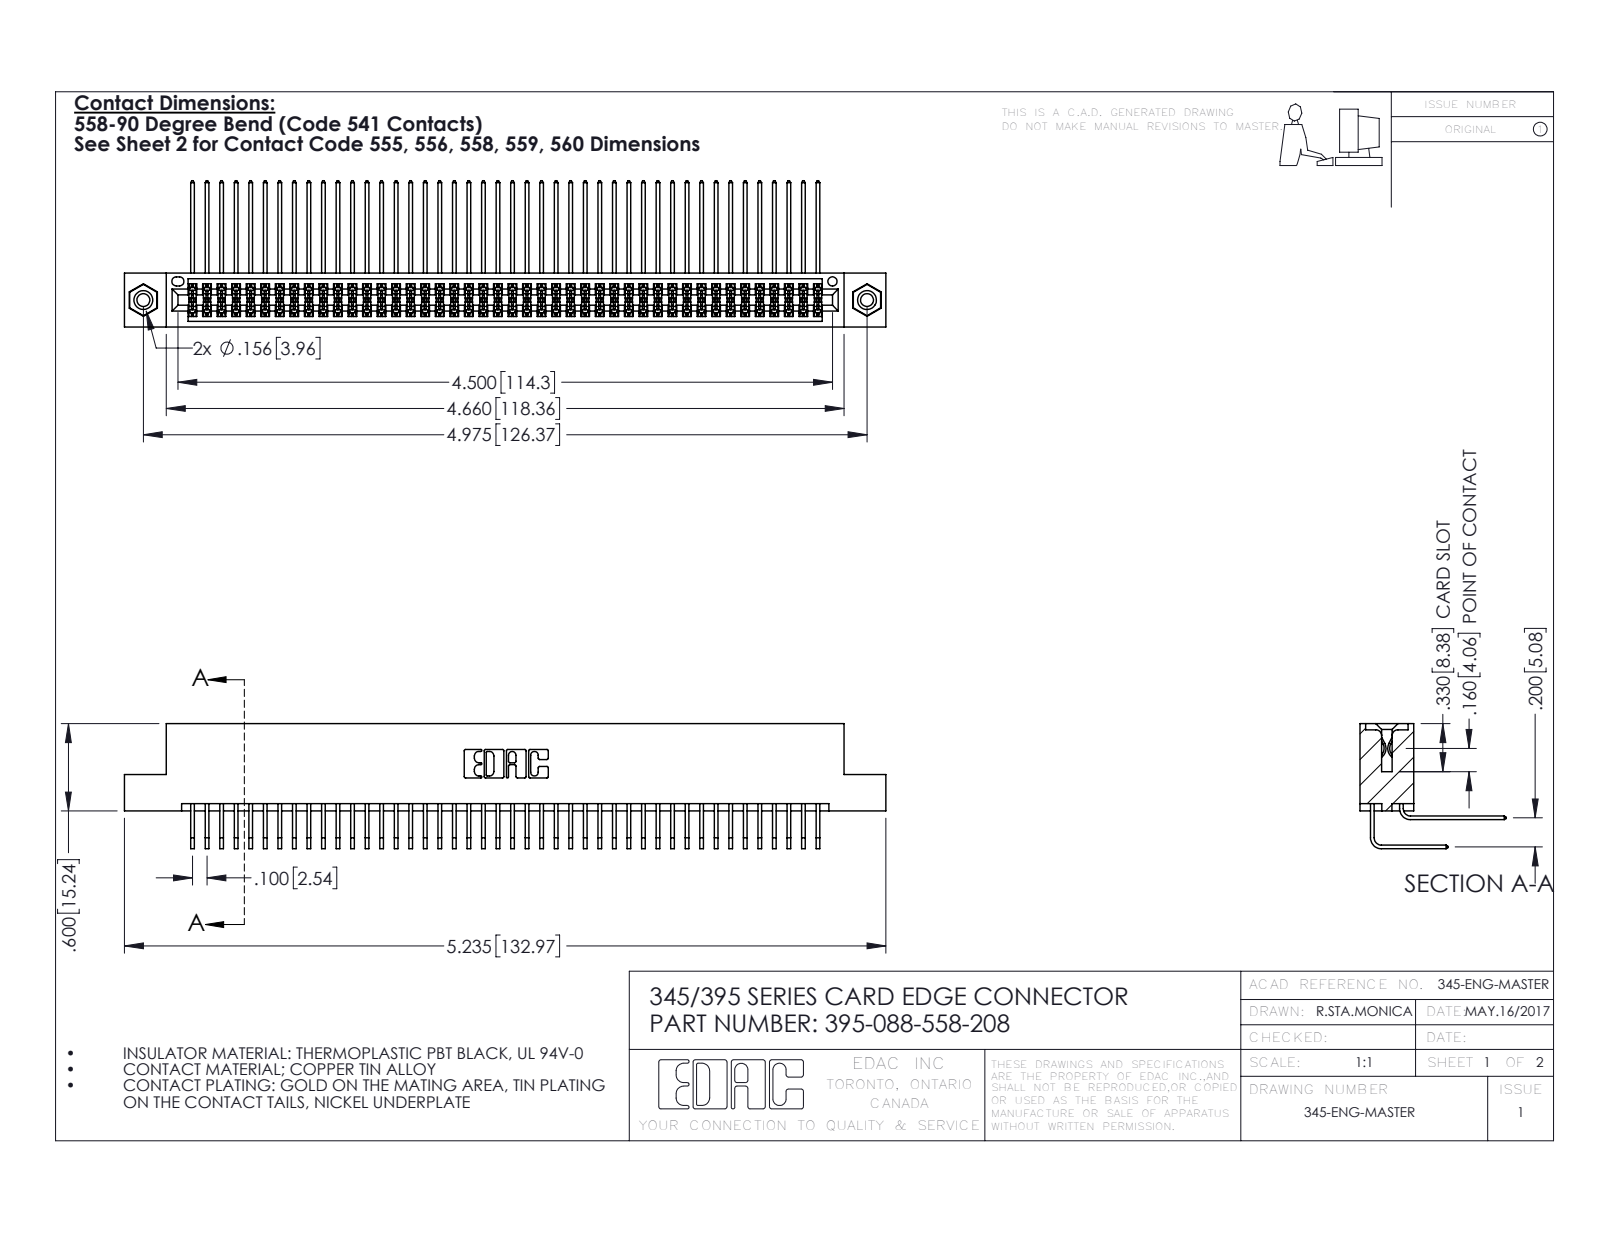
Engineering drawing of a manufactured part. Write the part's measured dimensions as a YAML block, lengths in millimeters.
part_name: "345-292-001_558 Tail - 2; 345-250-001_345-250-003-102; 345-292-001_558 559 Tail - 1; 395-088-558-208 (+1 more)"
step_written_by: "SolidWorks 2016 (CONFIG_CONTROL_DESIGN)"
units: millimeters
bodies: {solids: 91, faces: 4762, planar: 3192, cylindrical: 1554, other: 16}
overall_size: [133, 25.5, 21.8]
volume: 13400
surface_area: 22300
round_holes:
  - {diameter: 2.3, count: 2}
  - {diameter: 3.2, count: 2}
  - {diameter: 4, count: 2}
  - {diameter: 1.6, count: 1}
round_bosses_or_shafts:
  - {diameter: 3.9, count: 2}
partial_cylinders:
  - {radius: 0.2, count: 133}
  - {radius: 0.3, count: 22}
  - {radius: 0.2, count: 6}
  - {radius: 0.8, count: 6}
  - {radius: 0.7, count: 3}
  - {radius: 0.4, count: 2}
  - {radius: 0.5, count: 2}
  - {radius: 0.6, count: 2}
face_to_face_distances: [1.8, 7.6, 5.1, 9.4, 2.5, 6.9, 0.6, 5.7, 0.6, 4.4]
hole_center_spacings: [6.9, 120.4, 126.4]
